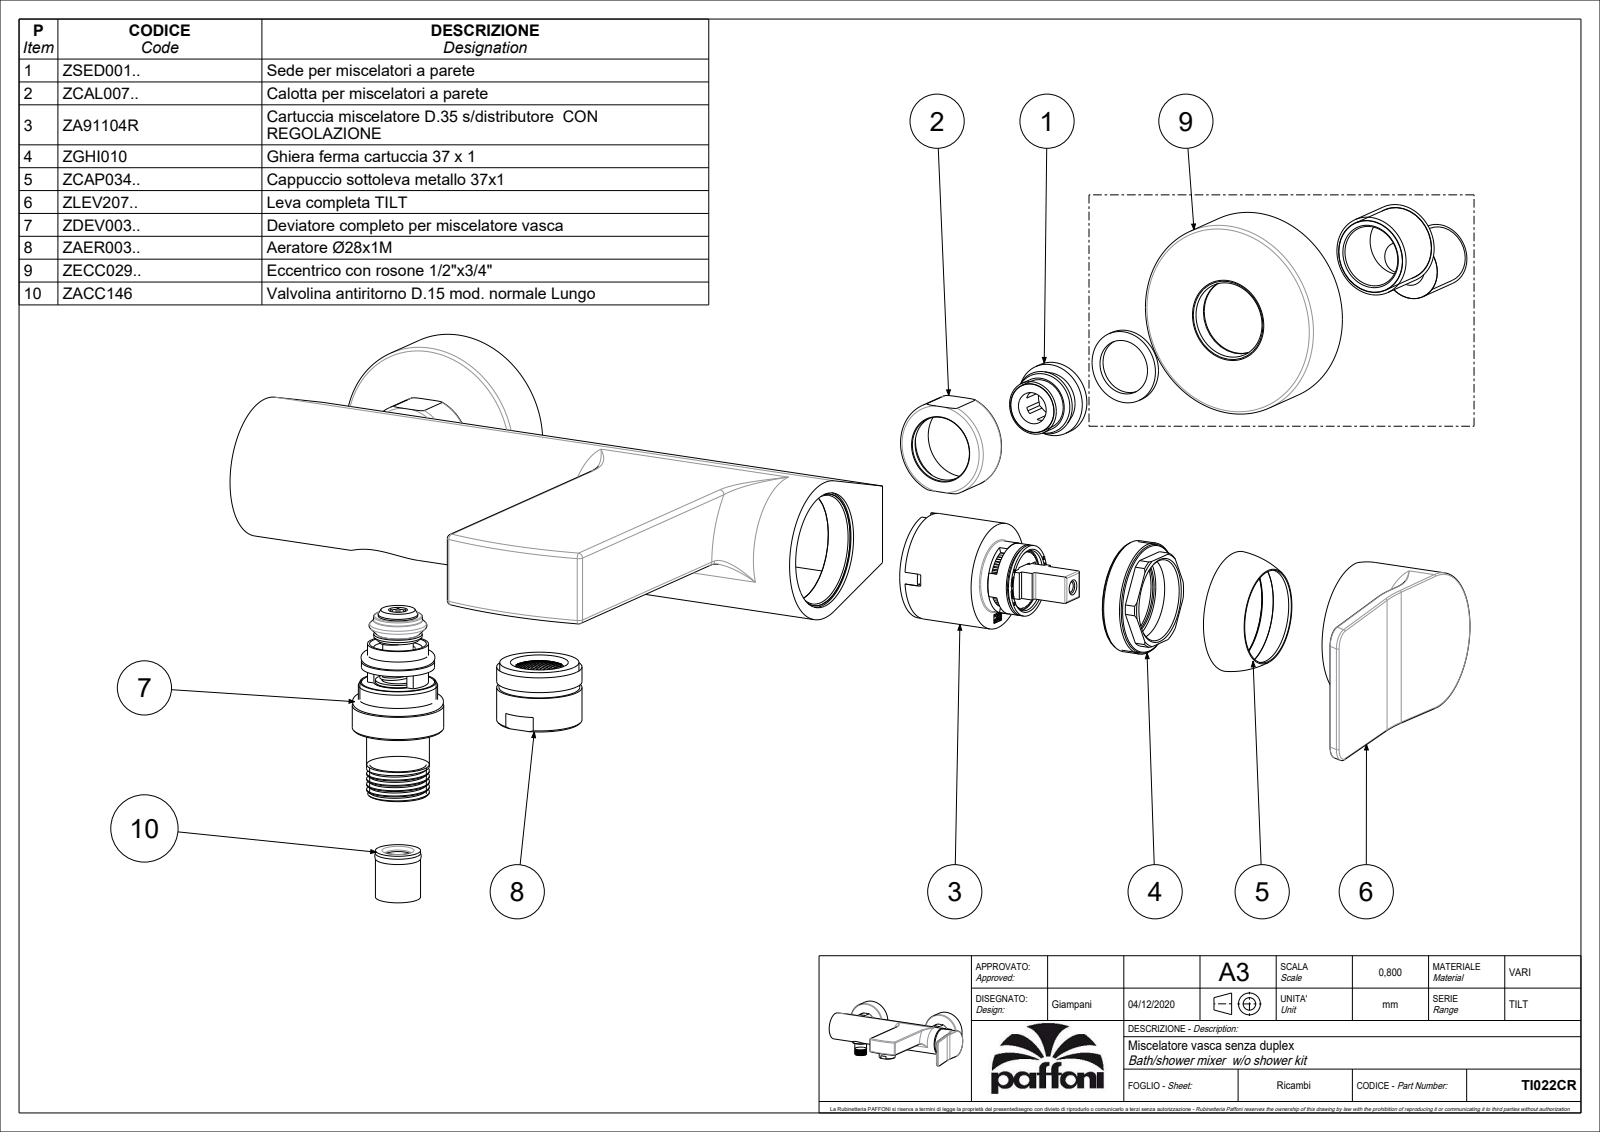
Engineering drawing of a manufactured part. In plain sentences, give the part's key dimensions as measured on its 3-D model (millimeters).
The part is named "TI022CR". Its 3-D file was written by "CREO PARAMETRIC BY PTC INC, 2020044 (CONFIG_CONTROL_DESIGN)". It is 2 solids with 503 faces: 219 planar, 169 cylindrical and 115 other. Overall it measures 253.3 by 195.5 by 76.75 millimeters. Its volume is 439 591 cubic millimeters and its surface area 178 584 square millimeters. Round holes: 2 of diameter 10.5, 2 of diameter 16.5, 1 of diameter 3, 1 of diameter 3.5, 1 of diameter 4.2, 1 of diameter 7, 1 of diameter 8.5, 1 of diameter 9, 1 of diameter 11, 1 of diameter 14, 1 of diameter 15.1, 1 of diameter 16. Round bosses or shafts: 3 of diameter 24, 2 of diameter 63.5, 1 of diameter 45.5, 1 of diameter 37, 1 of diameter 30, 1 of diameter 28, 1 of diameter 27, 1 of diameter 26. Partial cylindrical surfaces (rounded edges, fillets, slot ends): 10 of radius 0.5, 8 of radius 1.5, 2 of radius 5, 2 of radius 15.6, 1 of radius 9.5, 1 of radius 10, 1 of radius 13, 1 of radius 19.5. The main face-to-face distances are 3.5, 31.5, 3, 34.5, 20.5, 48.5, 19, 15.5, 47.5, 13. The hole center spacings are 6, 51.6, 150, 154.02, 201.6.
